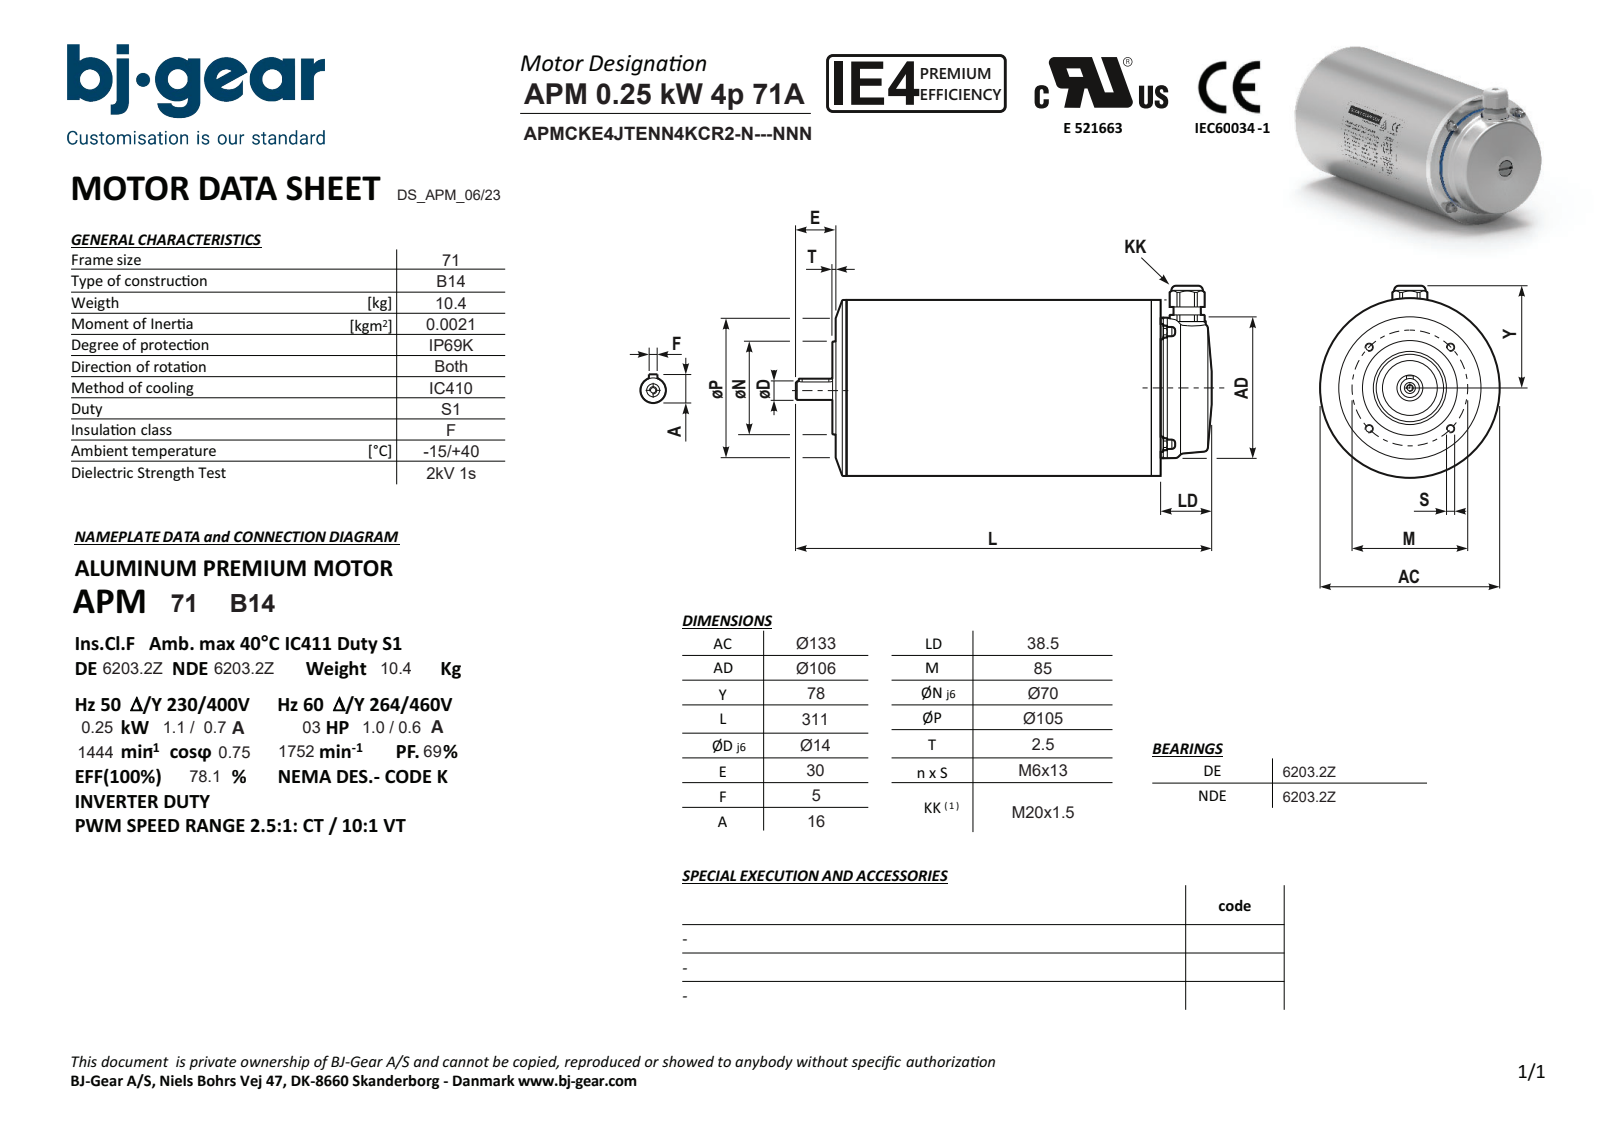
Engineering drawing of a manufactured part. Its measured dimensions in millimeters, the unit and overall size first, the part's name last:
Units: millimetres
Overall size (bounding box): 311 × 143.3 × 132.6
Round holes (diameter × count): ⌀4.92 ×4, ⌀4.13 ×1, ⌀5.3 ×1, ⌀16 ×1, ⌀28 ×1, ⌀52 ×1
Round bosses / shafts (diameter × count): ⌀11.5 ×4, ⌀7 ×4, ⌀132.6 ×1, ⌀132.6 ×1, ⌀106 ×1, ⌀70 ×1, ⌀23.7 ×1, ⌀20.6 ×1
Partial cylindrical surfaces — rounded edges, fillets, slot ends (radius × count): R2.5 ×2, R13.2 ×1
Main face-to-face distances: 242.5, 237, 5.5, 8, 2.5, 245, 283.5, 38.5, 275.5, 281
Hole centre spacings: 42.5, 60.1, 84.99
Volume: 3 639 000 mm³ · Surface area: 145 190 mm²
Bodies: 1 solid, 156 faces (71 planar, 50 cylindrical, 35 other)
Part name (STEP PRODUCT): APMCKE4JTENN4KCR2-N---NNN
STEP written by: Solid Edge (AUTOMOTIVE_DESIGN)
